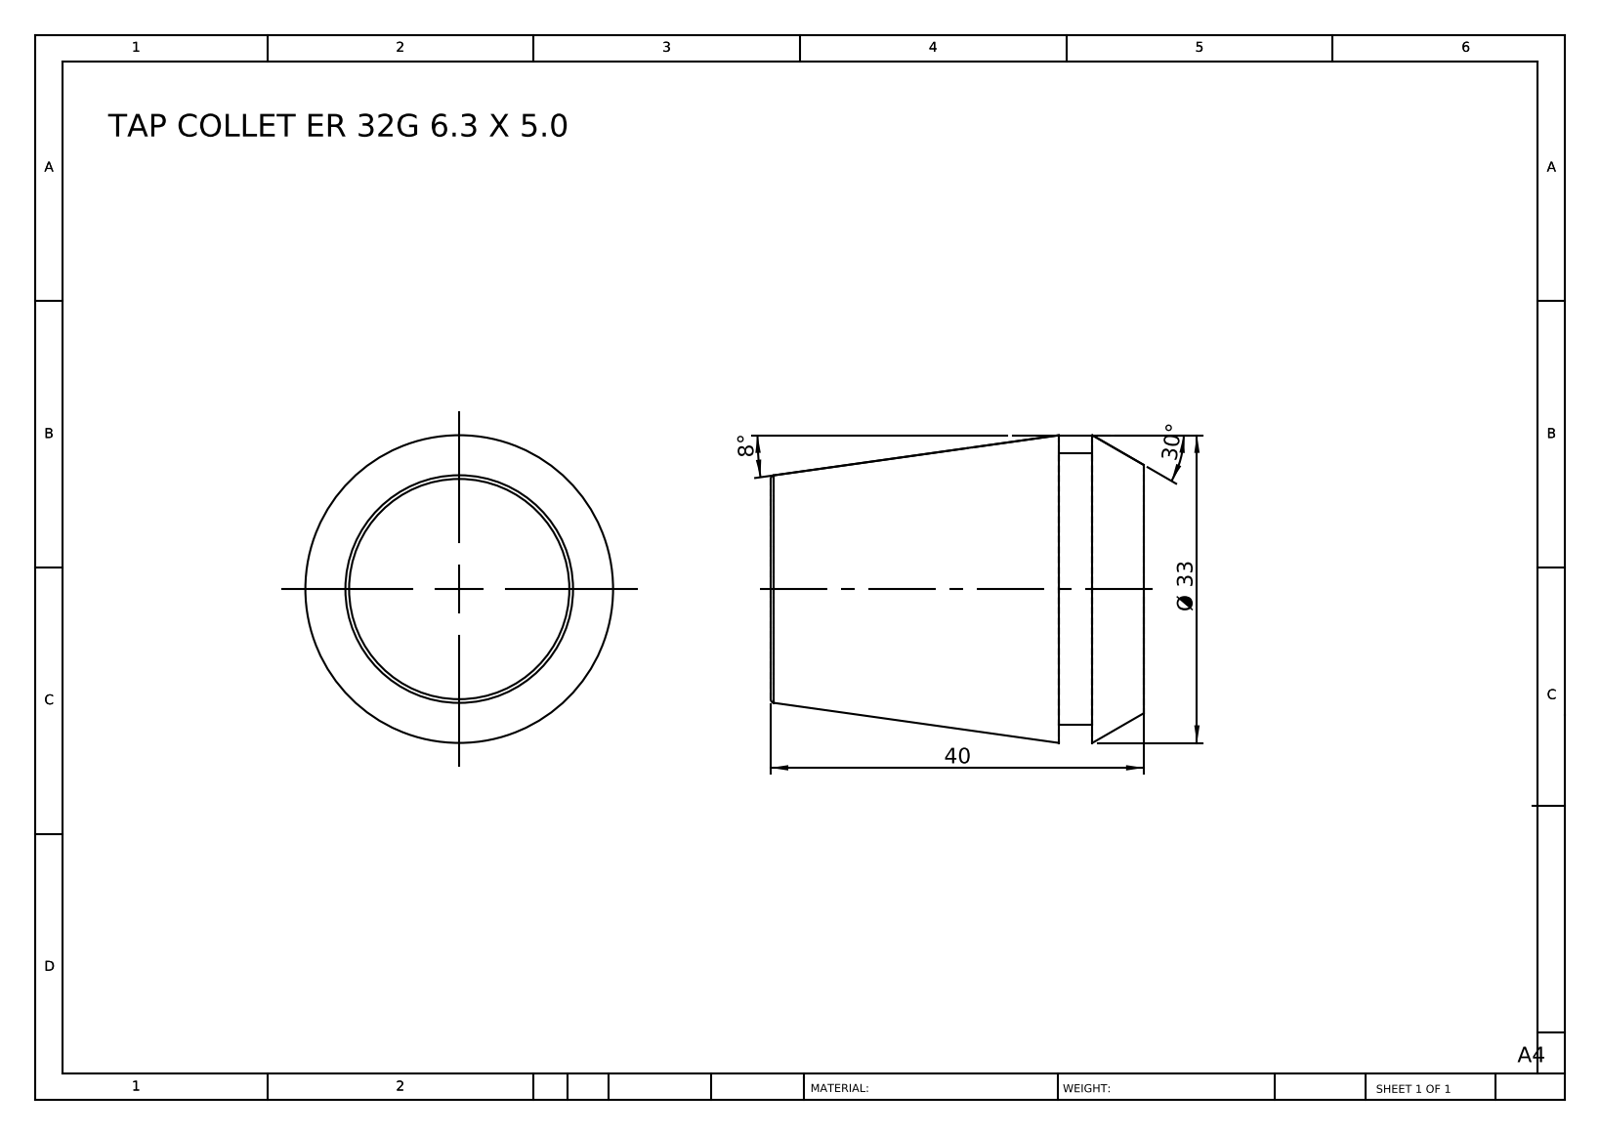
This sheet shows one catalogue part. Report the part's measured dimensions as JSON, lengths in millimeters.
{"part_name": "TAP COLLET ER 32G 6.3 X 5.0", "step_written_by": "SolidWorks 2014 (CONFIG_CONTROL_DESIGN)", "units": "millimeters", "bodies": {"solids": 1, "faces": 12, "planar": 4, "cylindrical": 2, "other": 6}, "overall_size": [40, 33, 33], "volume_mm3": 26350, "surface_area_mm2": 5119, "round_bosses_or_shafts": [[29.2, 1]], "face_to_face_distances": [40, 9.1, 30.9, 5.5, 3.6, 34.5]}
